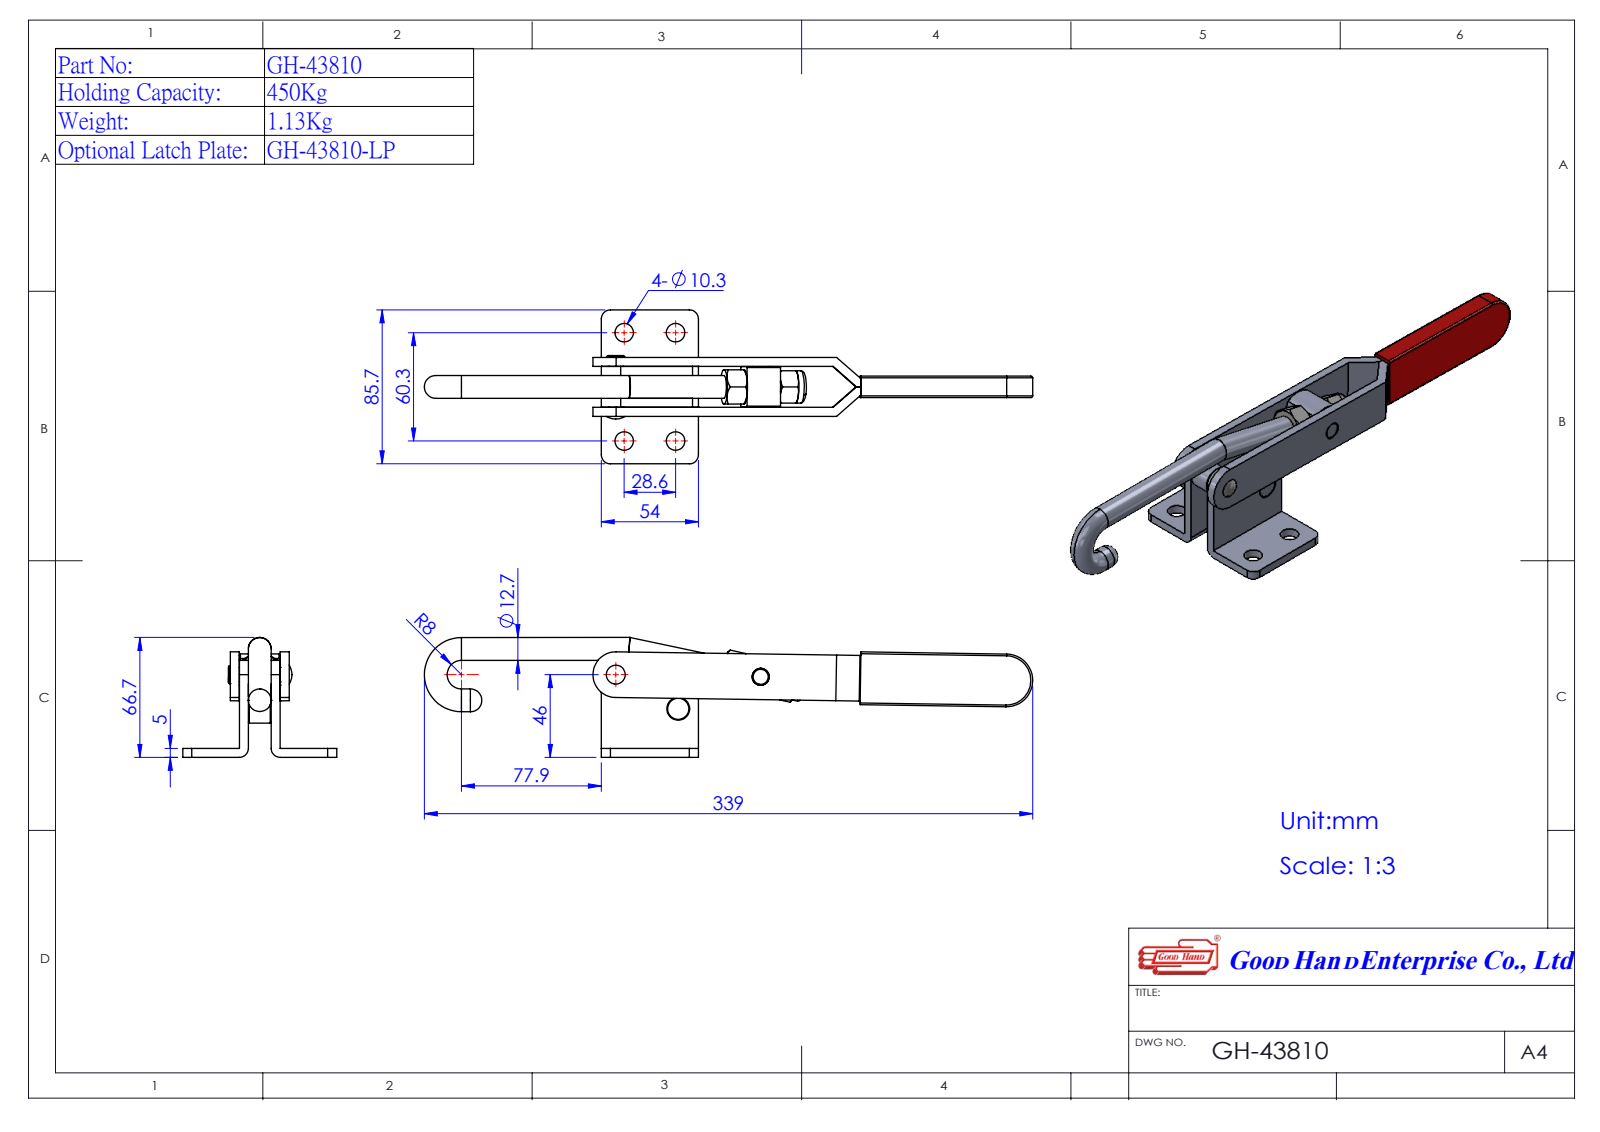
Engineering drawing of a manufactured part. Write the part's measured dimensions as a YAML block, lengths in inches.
part_name: "Group2^GH-43810(簡化); Group4^GH-43810(簡化); Group1^GH-43810(簡化); GH-43810(簡化) (+1 more)"
step_written_by: "SolidWorks 2016 (AUTOMOTIVE_DESIGN)"
units: inches
bodies: {solids: 4, faces: 185, planar: 69, cylindrical: 70, other: 46}
overall_size: [13.324, 3.378, 2.638]
volume: 9.752
surface_area: 97.96
round_holes:
  - {diameter: 0.406, count: 4}
  - {diameter: 0.236, count: 2}
  - {diameter: 0.422, count: 1}
  - {diameter: 0.425, count: 1}
  - {diameter: 0.472, count: 1}
  - {diameter: 0.5, count: 1}
  - {diameter: 0.54, count: 1}
  - {diameter: 0.594, count: 1}
round_bosses_or_shafts:
  - {diameter: 0.5, count: 3}
  - {diameter: 0.63, count: 2}
  - {diameter: 0.709, count: 1}
  - {diameter: 0.394, count: 1}
partial_cylinders:
  - {radius: 0.197, count: 7}
  - {radius: 0.5, count: 2}
  - {radius: 0.579, count: 1}
face_to_face_distances: [0.197, 0.898, 1.094, 0.409, 0.882, 0.213, 0.685, 0.394, 0.701, 0.016]
hole_center_spacings: [1.126, 2.378, 2.631, 3.177]
